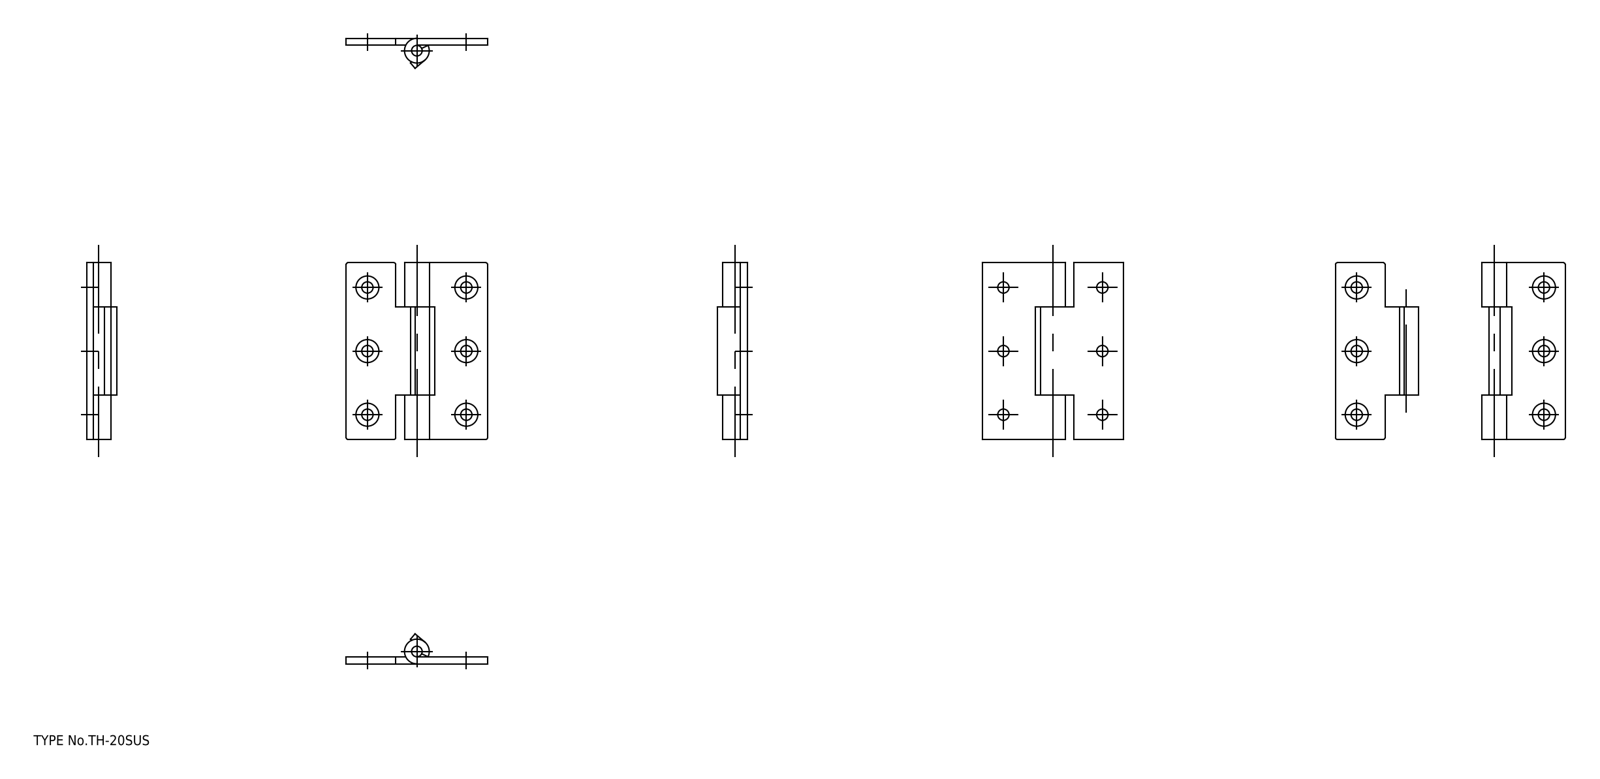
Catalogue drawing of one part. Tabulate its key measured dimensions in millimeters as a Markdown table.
| quantity | value |
| --- | --- |
| part name | shaft; hinge piece_B; hinge piece_A |
| STEP written by | spGate 19.8.4 (****-****-****-****) (AUTOMOTIVE_DESIGN) |
| units | millimeters |
| bodies | 3 solids, 62 faces (24 planar, 26 cylindrical, 12 other) |
| overall size | 50 × 40 × 8.5 |
| volume | 4 724 mm³ |
| surface area | 5 769 mm² |
| round holes (diameter × count) | 3.2 × 6, 3 × 1 |
| round bosses / shafts (diameter × count) | 7 × 1 |
| partial cylindrical surfaces (radius × count) | 0.5 × 6 |
| main face-to-face distances | 2, 12.5, 37.5, 25, 40, 50, 15, 14, 11, 26 |
| hole center spacings | 18, 33.29, 28, 36, 45.61 |
